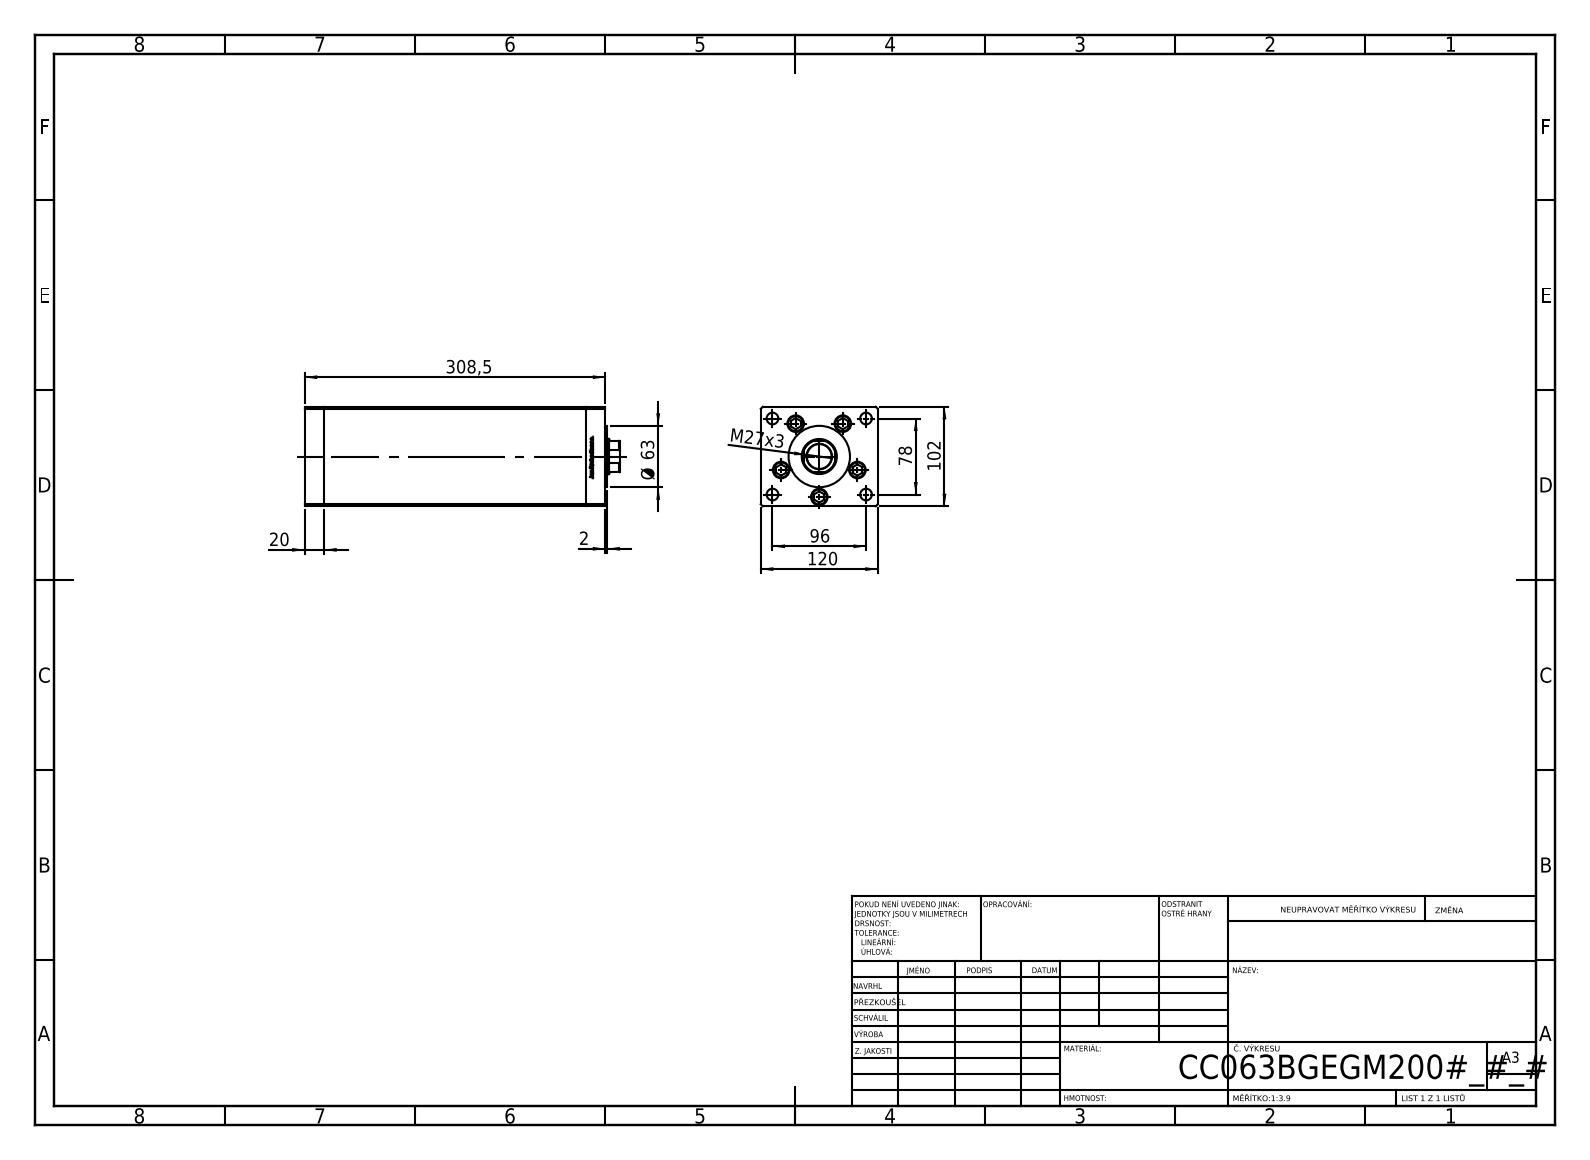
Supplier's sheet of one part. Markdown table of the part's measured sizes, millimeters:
| quantity | value |
| --- | --- |
| part name | V220C_VC_B; V220C BACK_B; V220C_FRONT_B; V220C_B MIDDLE (+1 more) |
| STEP written by | SolidWorks 2019 (CONFIG_CONTROL_DESIGN) |
| units | millimeters |
| bodies | 14 solids, 1185 faces (464 planar, 147 cylindrical, 574 other) |
| overall size | 323.5 × 120 × 102 |
| volume | 3 241 000 mm³ |
| surface area | 348 937 mm² |
| round holes (diameter × count) | 13.5 × 5, 17 × 5, 12 × 4, 2 × 2, 13.16 × 2, 25.5 × 1, 36 × 1 |
| round bosses / shafts (diameter × count) | 8 × 5, 63 × 1 |
| partial cylindrical surfaces (radius × count) | 0.93 × 2, 17.5 × 1 |
| main face-to-face distances | 120, 102, 20, 268.5, 288.5, 34.25, 308.5, 14.25, 254.25, 274.25 |
| hole center spacings | 41.5, 61.85, 24.39, 26.69, 47.92, 48.07, 49.84, 53.57 |
